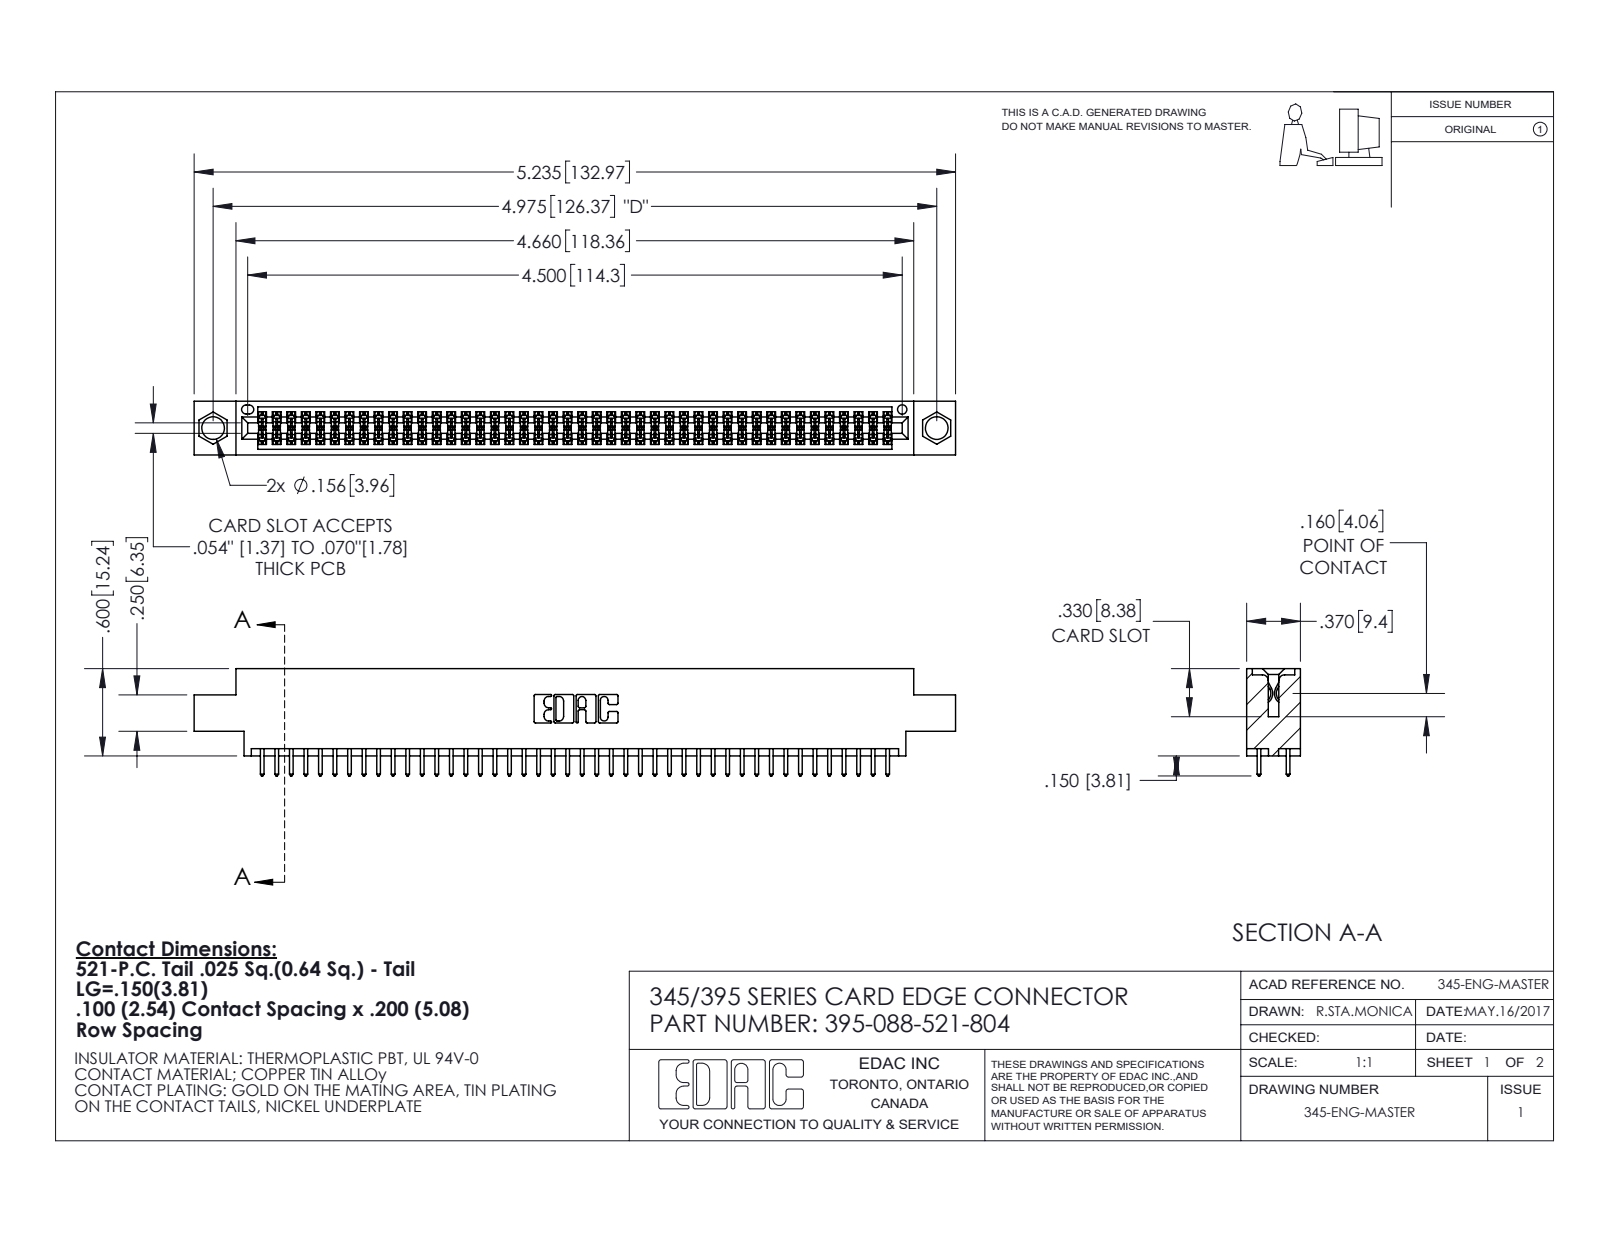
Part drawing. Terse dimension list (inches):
name: 395-088-521-804; 345-292-001_345-293-121; 345 Part_0.170 Offset - 0.156 Dia-TI
written by: SolidWorks 2020 (CONFIG_CONTROL_DESIGN)
unit: in
bodies: 89 solids, 4544 faces (3002 planar, 1542 cylindrical, 0 other)
size: 5.235 × 0.737 × 0.37
volume: 0.774 in³; area: 28.74 in²
holes: 2× ⌀0.156, 1× ⌀0.064
rounds: 176× R0.006, 88× R0.01, 22× R0.01, 6× R0.007, 6× R0.031, 3× R0.026, 2× R0.014, 2× R0.019
face distances: 0.072, 0.298, 0.2, 0.37, 0.098, 0.272, 0.025, 0.225, 0.175, 0.149
hole spacings: 0.27, 4.739, 4.975
